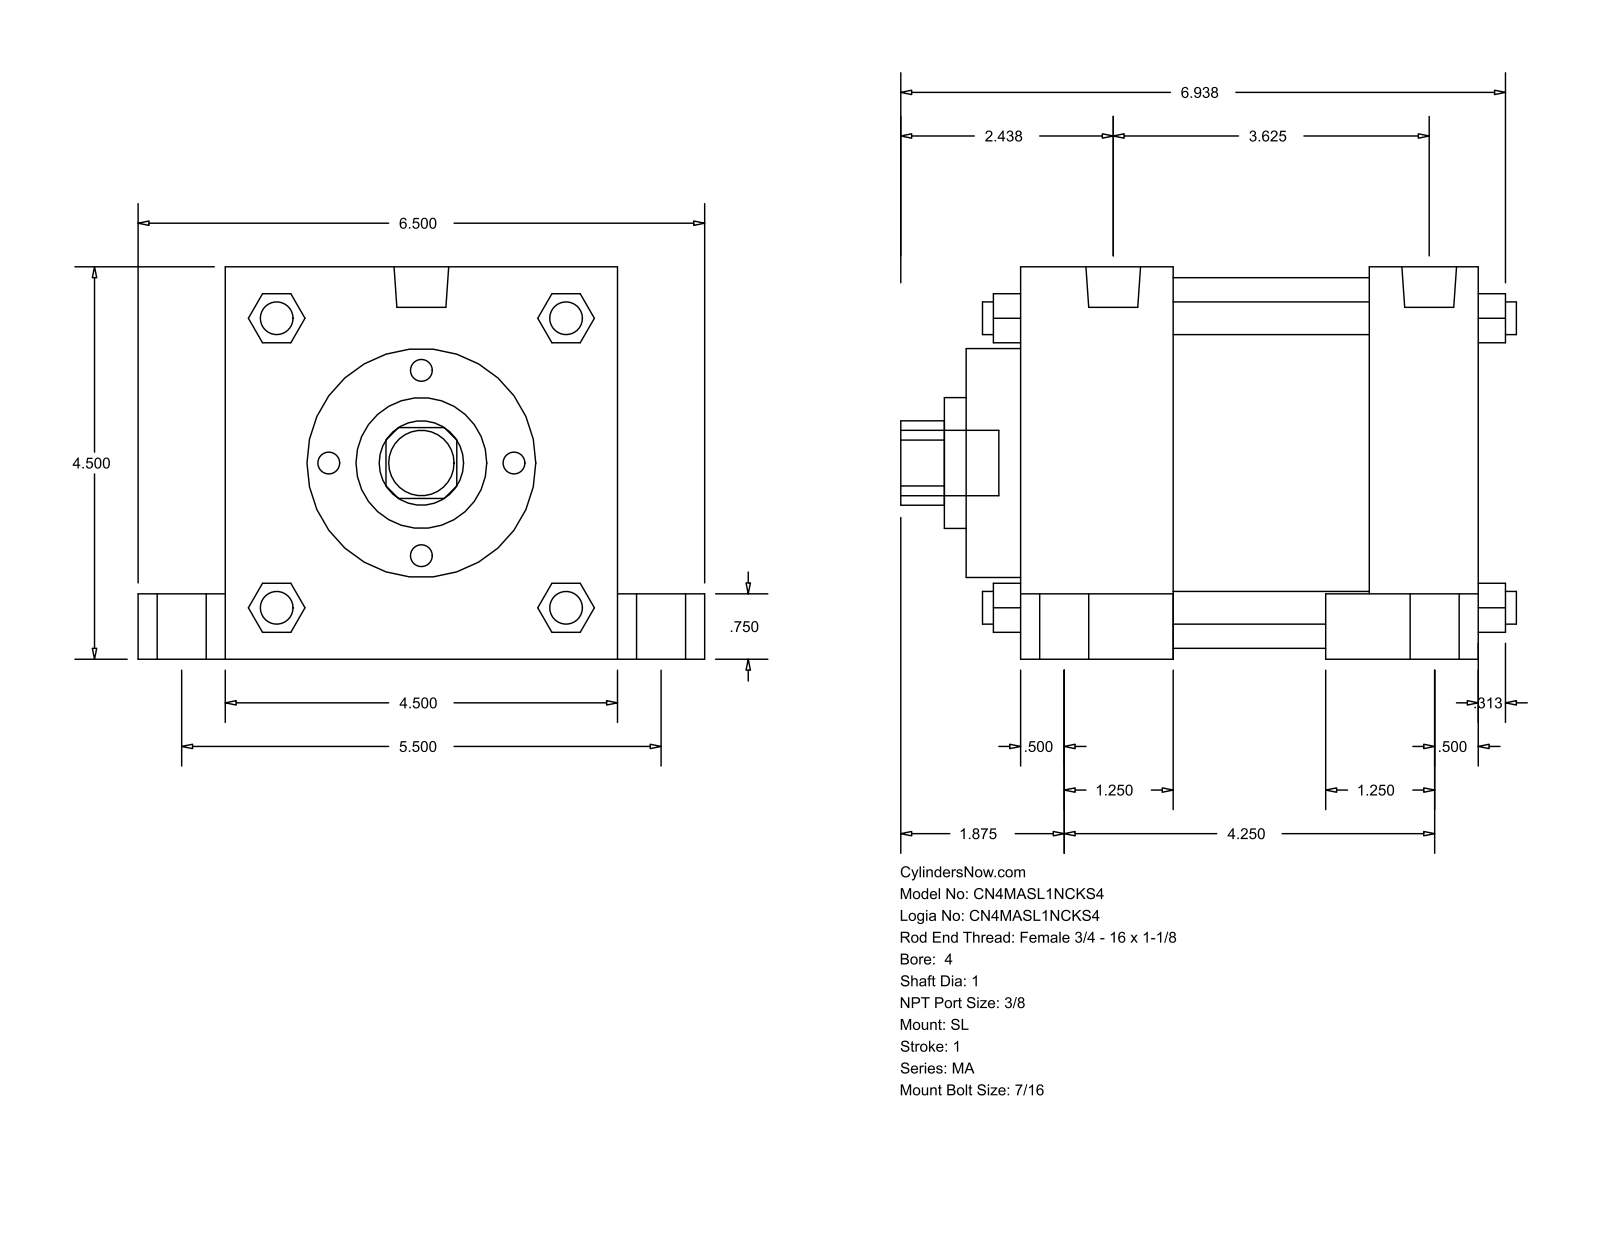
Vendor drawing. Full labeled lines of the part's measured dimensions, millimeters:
Part name (STEP PRODUCT): MA_SL__0400_1
STEP written by: GSSL Pune (CONFIG_CONTROL_DESIGN)
Units: millimetres
Bodies: 0 solids, 150 faces (113 planar, 37 cylindrical, 0 other)
Overall size (bounding box): 179.39 × 165.1 × 114.3
Round holes (diameter × count): ⌀25.4 ×1, ⌀38.1 ×1, ⌀66.67 ×1, ⌀107.95 ×1
Round bosses / shafts (diameter × count): ⌀20.64 ×4, ⌀14.29 ×4, ⌀11.11 ×4, ⌀9.53 ×4, ⌀15.93 ×2, ⌀19.05 ×1
Partial cylindrical surfaces — rounded edges, fillets, slot ends (radius × count): R12.29 ×1
Main face-to-face distances: 114.3, 133.36, 57.15, 44.46, 88.9, 101.61, 31.75, 25.4, 139.7, 19.05
